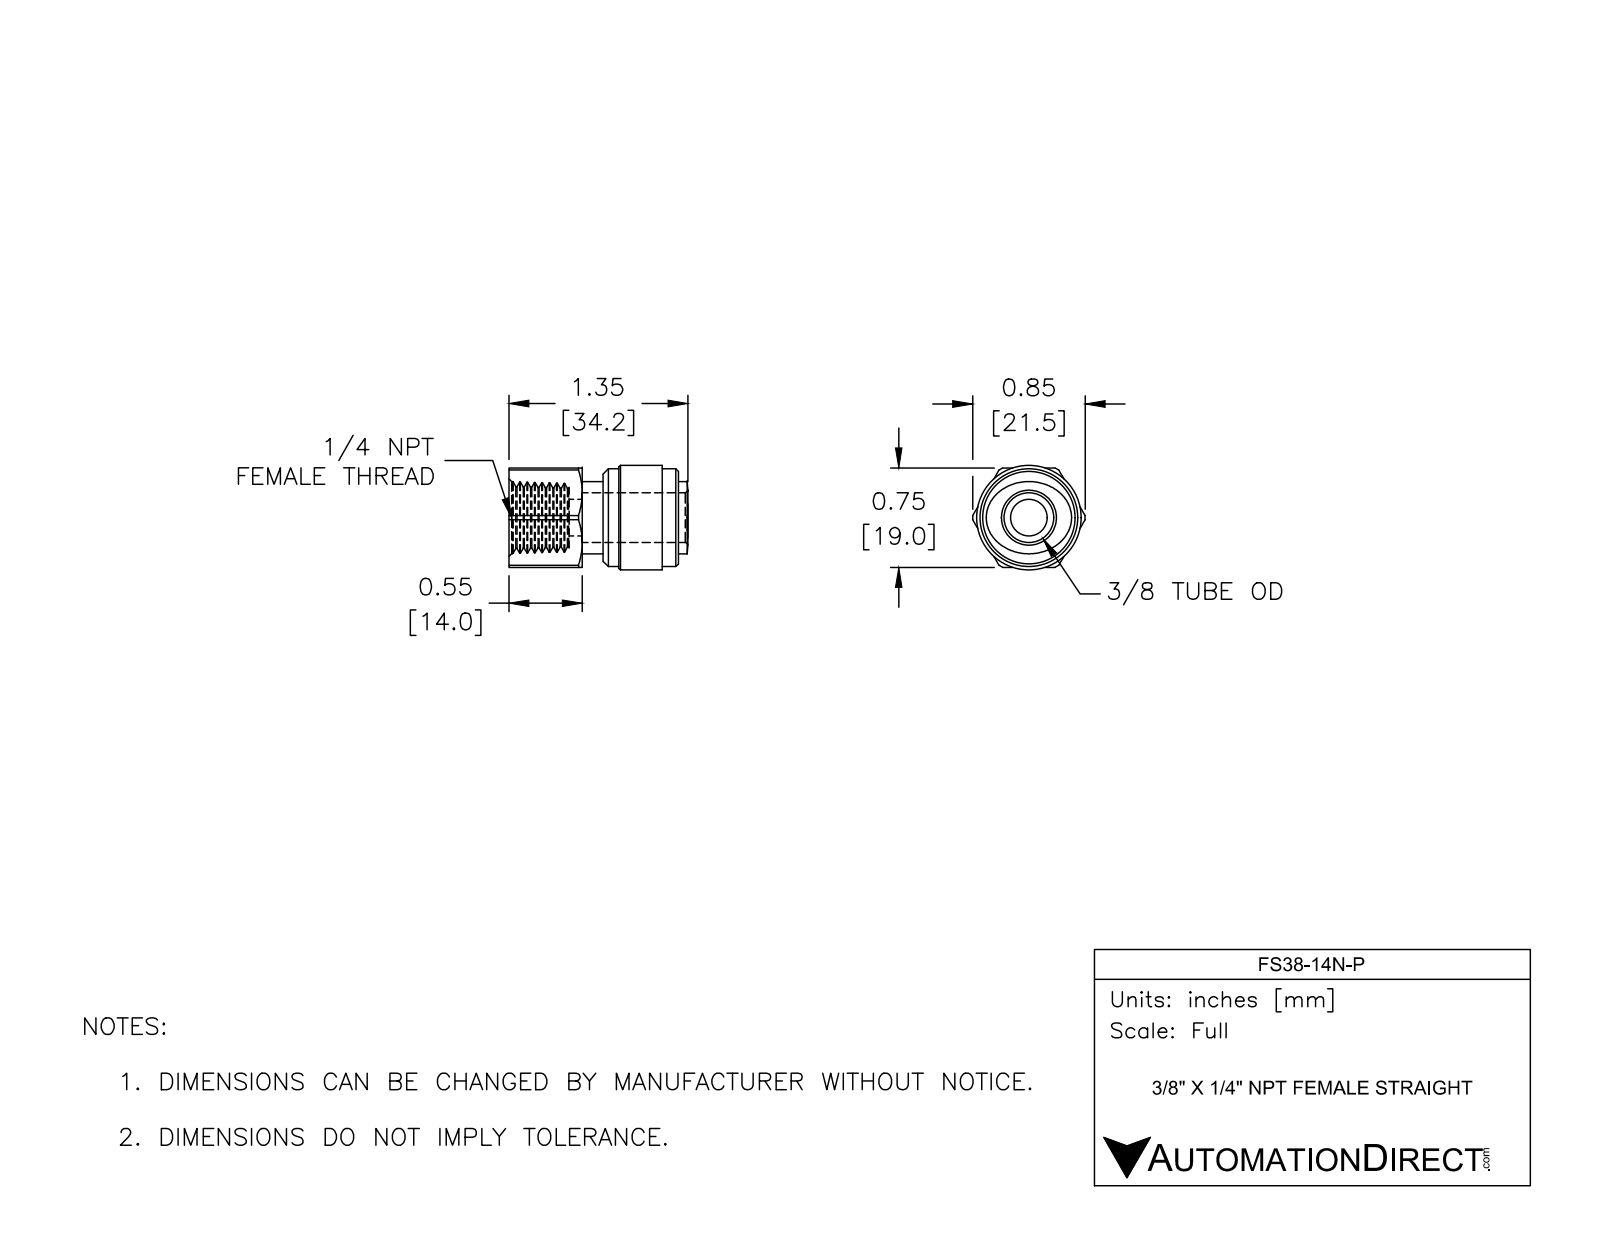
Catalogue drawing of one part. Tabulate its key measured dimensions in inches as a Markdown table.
| quantity | value |
| --- | --- |
| part name | FS38-14N-P |
| STEP written by | SolidWorks 2017 (AUTOMOTIVE_DESIGN) |
| units | inches |
| bodies | 1 solid, 134 faces (14 planar, 19 cylindrical, 101 other) |
| overall size | 1.347 × 0.846 × 0.787 |
| volume | 0.402 in³ |
| surface area | 6.545 in² |
| round holes (diameter × count) | 0.276 × 1, 0.374 × 1 |
| round bosses / shafts (diameter × count) | 0.787 × 1, 0.736 × 1, 0.543 × 1 |
| partial cylindrical surfaces (radius × count) | 0.423 × 1 |
| main face-to-face distances | 0.748, 0.551, 0.709, 0.157, 1.276, 0.724, 0.567, 0.453, 0.098, 0.256 |
